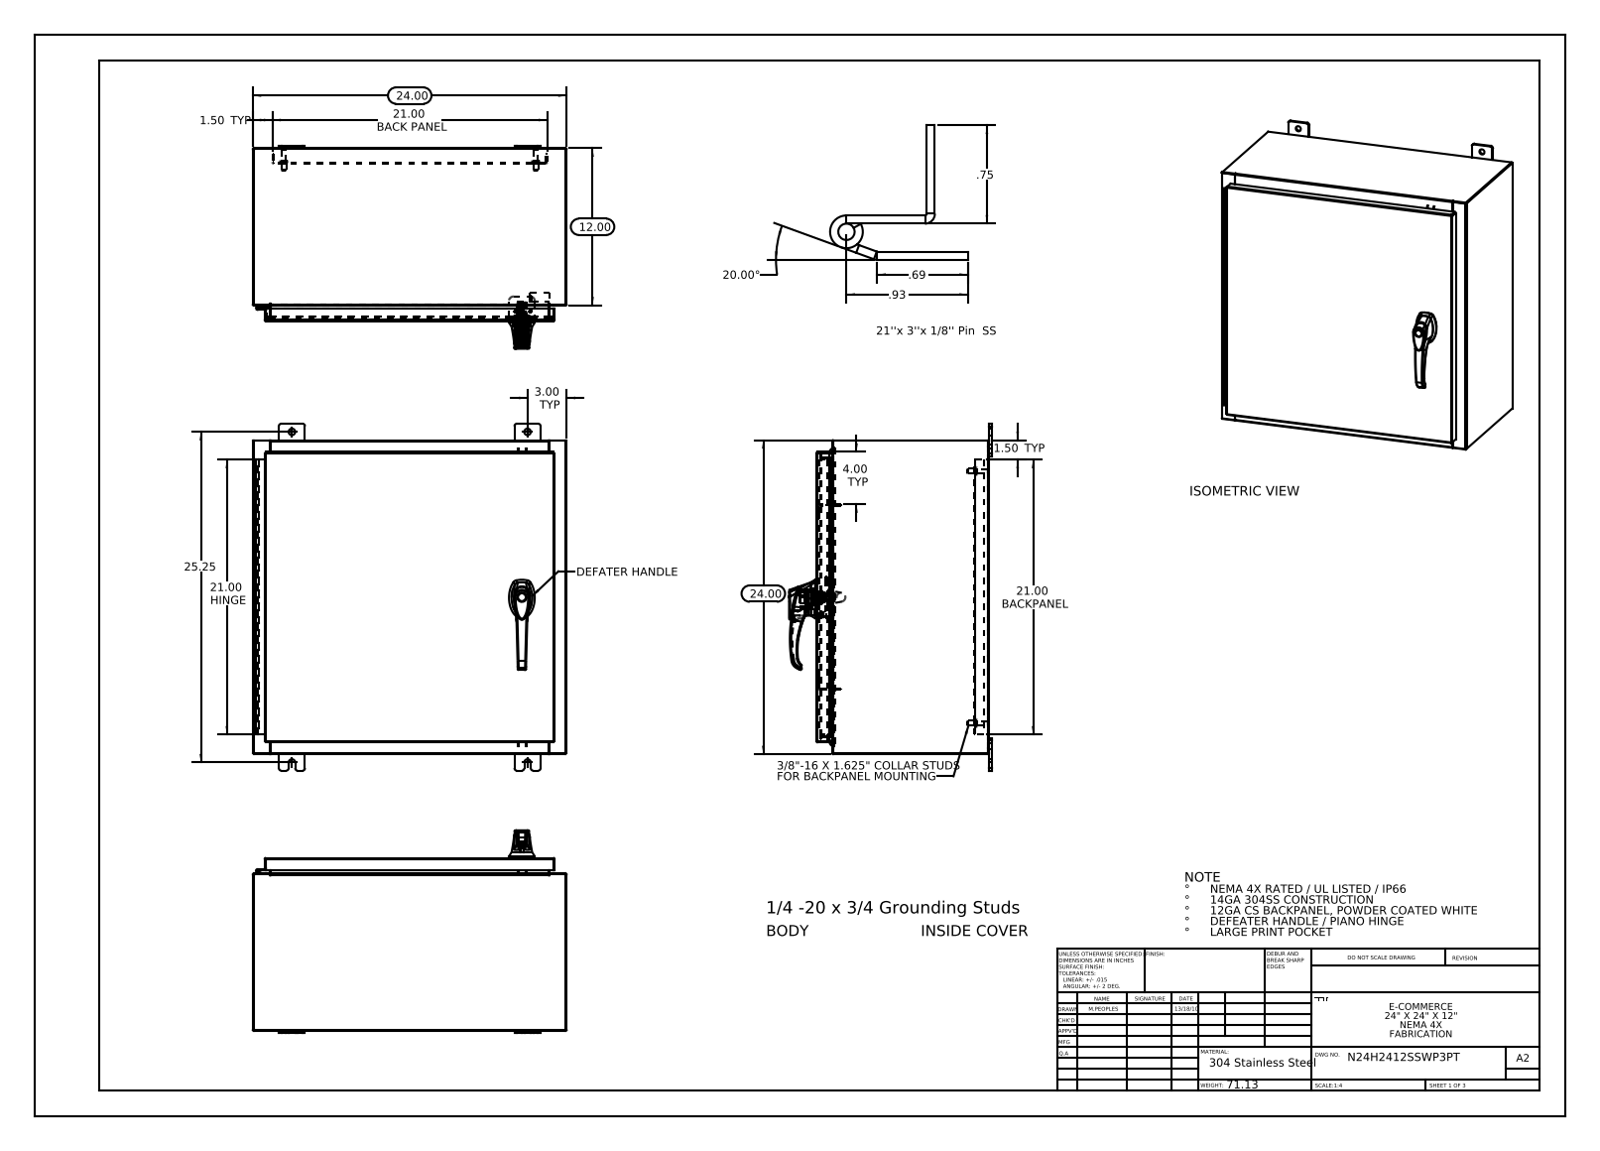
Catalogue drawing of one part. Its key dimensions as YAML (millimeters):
part_name: "N24H2412SSWP3PT Top; N24H2412SSWP3PT 125 Pin Hinge; N24H2412SSWP3PT Cover; N24H2412SSWP3PT Hinge Cover Side (+8 more)"
step_written_by: "SolidWorks 2013 (CONFIG_CONTROL_DESIGN)"
units: millimeters
bodies: {solids: 31, faces: 2412, planar: 865, cylindrical: 893, other: 654}
overall_size: [673.1, 609.6, 393.6]
volume: 4126000
surface_area: 4055000
round_holes:
  - {diameter: 12.7, count: 8}
  - {diameter: 6.4, count: 4}
  - {diameter: 3.5, count: 3}
  - {diameter: 4.1, count: 3}
  - {diameter: 2, count: 2}
  - {diameter: 5.2, count: 2}
  - {diameter: 8, count: 2}
  - {diameter: 11.1, count: 2}
  - {diameter: 3.2, count: 1}
  - {diameter: 3.2, count: 1}
  - {diameter: 5, count: 1}
  - {diameter: 7, count: 1}
round_bosses_or_shafts:
  - {diameter: 15.9, count: 4}
  - {diameter: 9.5, count: 4}
  - {diameter: 8.4, count: 4}
  - {diameter: 30, count: 1}
  - {diameter: 19, count: 1}
  - {diameter: 17.3, count: 1}
  - {diameter: 16.8, count: 1}
  - {diameter: 16.2, count: 1}
partial_cylinders:
  - {radius: 3, count: 37}
  - {radius: 0.2, count: 33}
  - {radius: 4.8, count: 24}
  - {radius: 0.3, count: 22}
  - {radius: 2.2, count: 18}
  - {radius: 1, count: 15}
  - {radius: 0.7, count: 12}
  - {radius: 0.2, count: 6}
face_to_face_distances: [1.9, 607.7, 333.4, 605.8, 609.6, 331.5, 335.3, 2.6, 25.4, 27.3]
hole_center_spacings: [195.1, 7.5, 15.9, 21.4, 31.8, 33.4, 39.6, 47.2]
